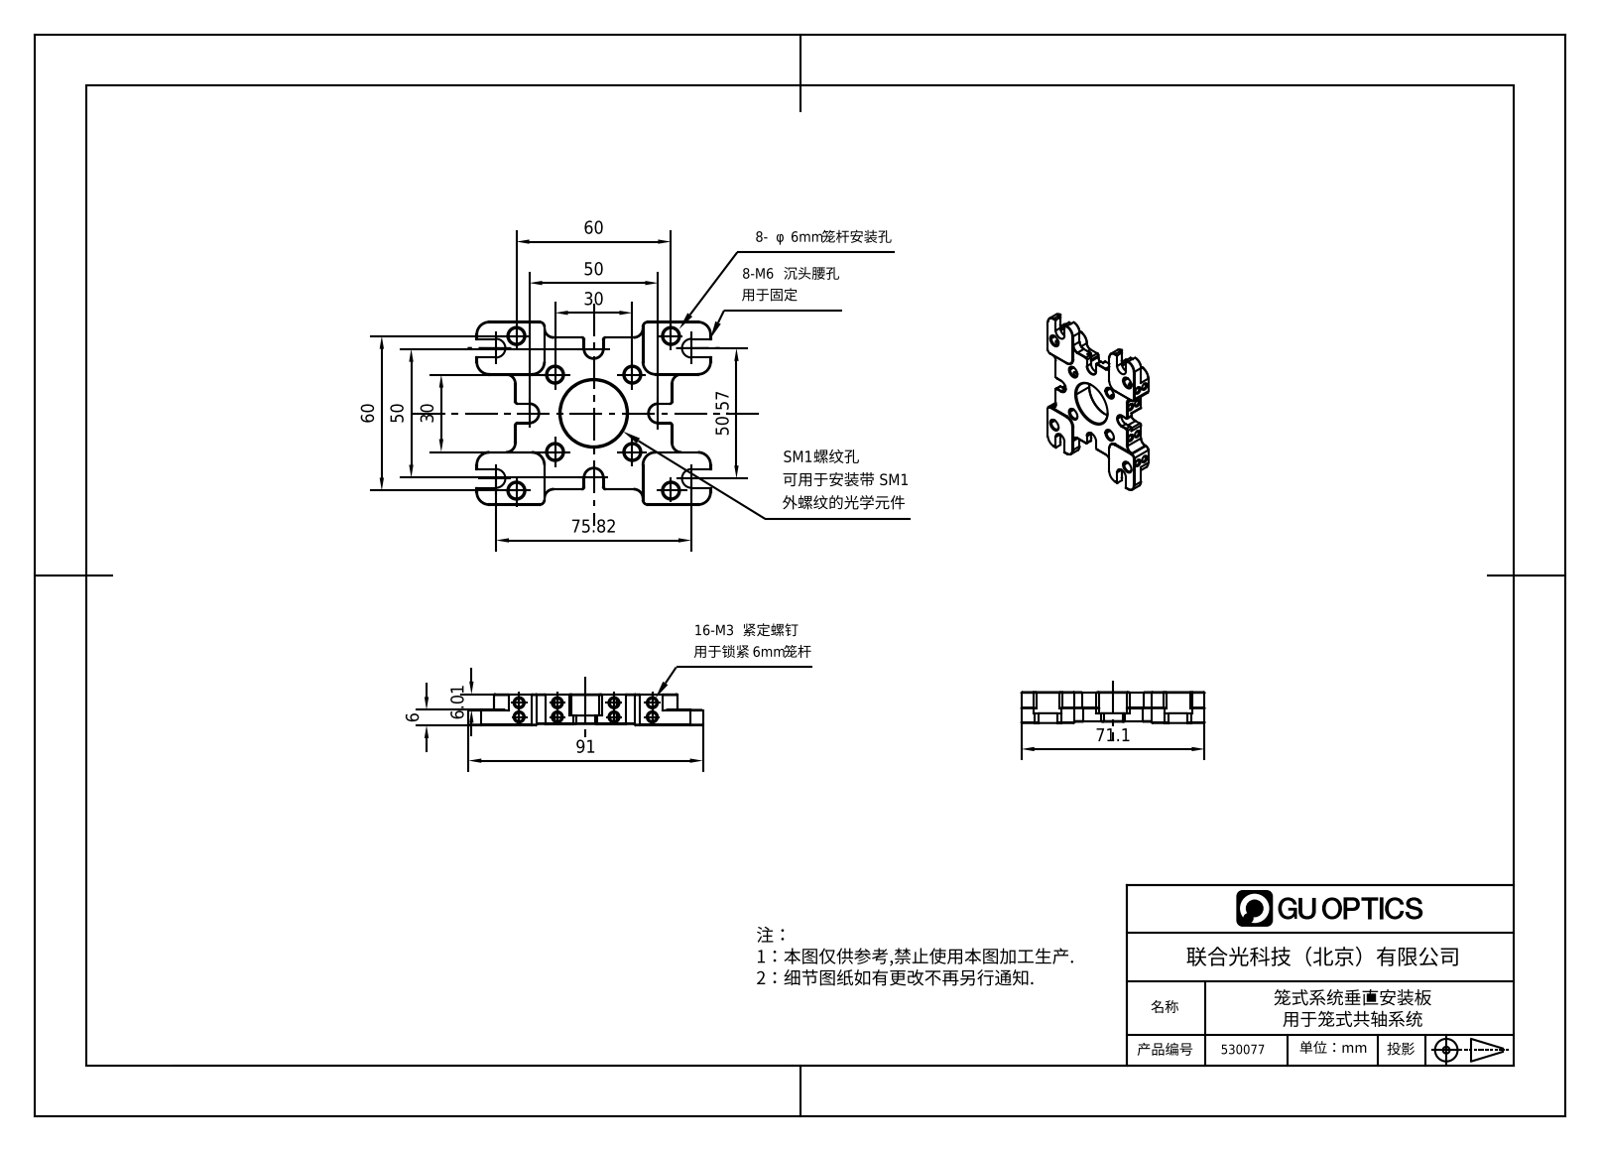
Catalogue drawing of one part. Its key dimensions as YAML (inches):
part_name: "2.4.4.10_LZA-Z_笼式系统垂直安装板，用于笼式共轴系统"
step_written_by: "SolidWorks 2018 (AUTOMOTIVE_DESIGN)"
units: inches
bodies: {solids: 0, faces: 644, planar: 234, cylindrical: 132, other: 278}
overall_size: [3.583, 2.799, 0.472]
round_holes:
  - {diameter: 0.13, count: 8}
  - {diameter: 0.236, count: 8}
  - {diameter: 1.01, count: 1}
partial_cylinders:
  - {radius: 0.039, count: 28}
  - {radius: 0.197, count: 12}
  - {radius: 0.138, count: 8}
  - {radius: 0.143, count: 8}
  - {radius: 0.213, count: 8}
  - {radius: 0.219, count: 8}
  - {radius: 0.079, count: 4}
  - {radius: 0.118, count: 4}
face_to_face_distances: [0.453, 0.472, 0.02, 0.236, 0.217, 0.323, 0.087, 0.13, 0.15, 2.563]
hole_center_spacings: [0.835, 1.867, 1.67, 0.217, 0.585, 0.624, 1.181, 1.451]
